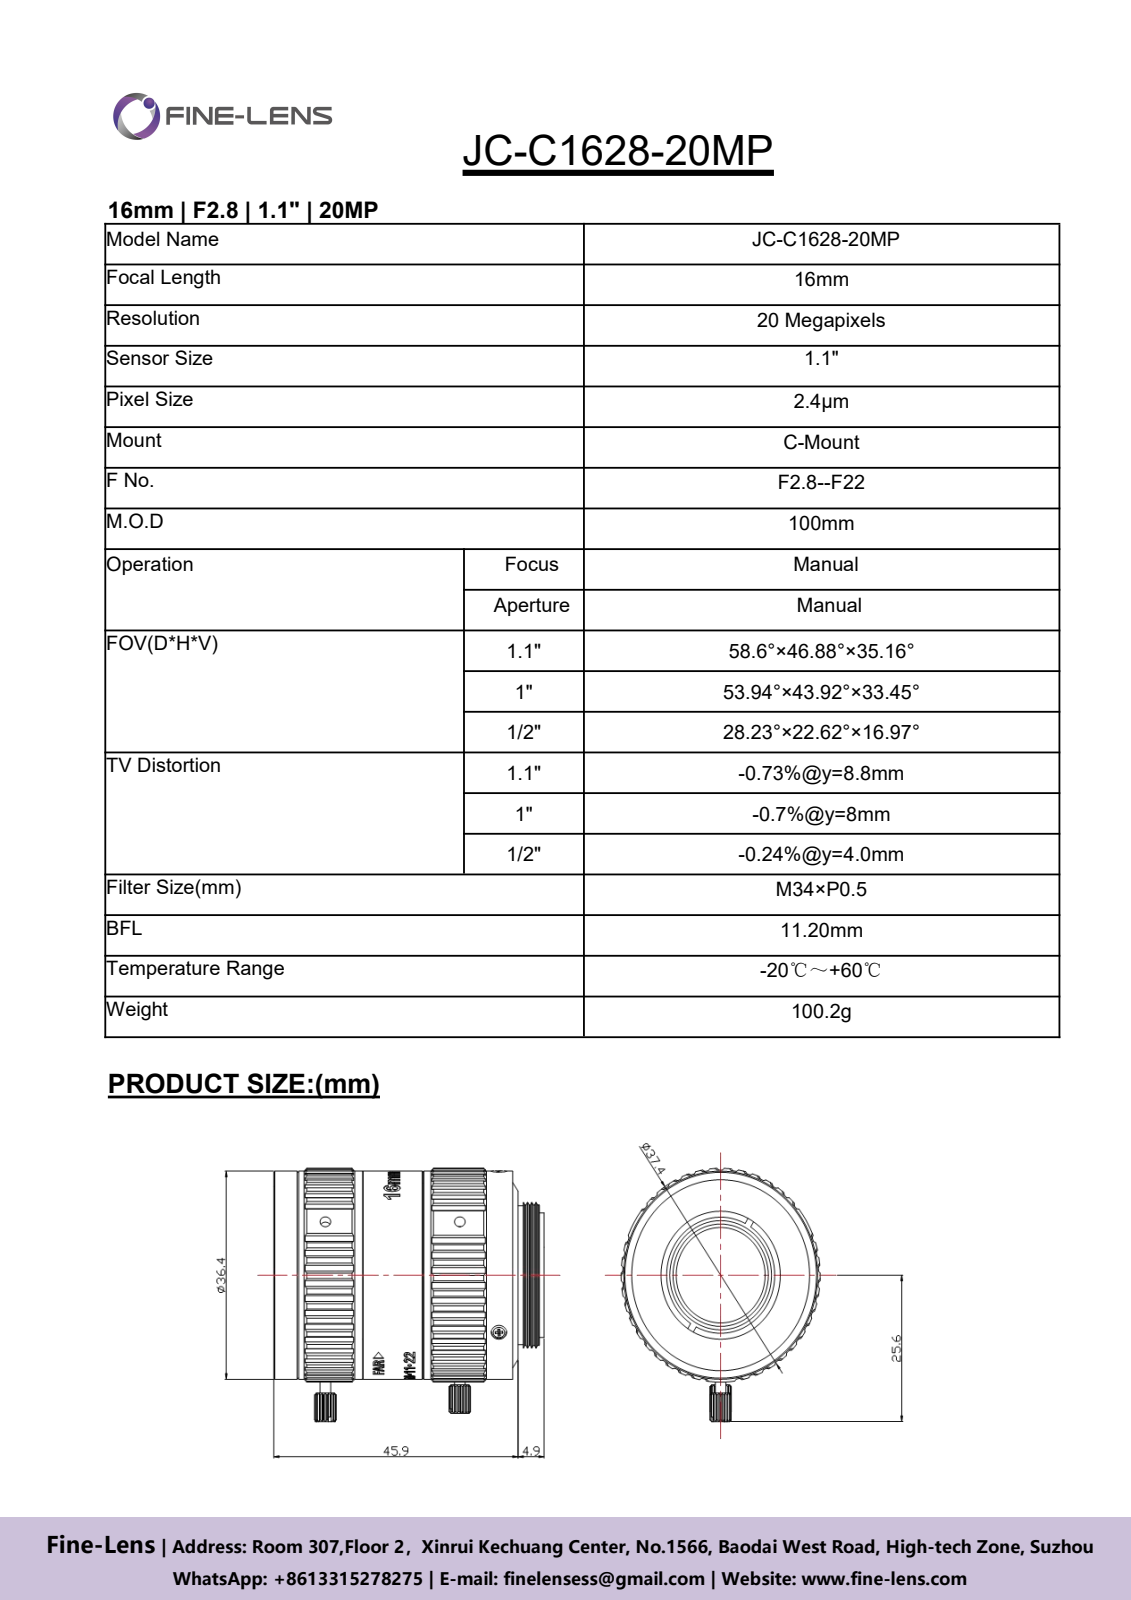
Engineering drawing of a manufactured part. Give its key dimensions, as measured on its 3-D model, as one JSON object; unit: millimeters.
{"part_name": "16MM_1_1INCH_ASM; 16MM_1_1INCH_ASM_ASM", "step_written_by": "CREO PARAMETRIC BY PTC INC, 2020053 (CONFIG_CONTROL_DESIGN)", "units": "millimeters", "bodies": {"solids": 1, "faces": 1450, "planar": 661, "cylindrical": 385, "other": 404}, "overall_size": [50.77, 41.66, 37.39], "volume_mm3": 24148, "surface_area_mm2": 26913, "round_holes": [[2, 6], [1.4, 4], [1.2, 3], [1.7, 3], [2.9, 3], [3, 3], [1.5, 2], [2.6, 2], [12.4, 1], [14.8, 1], [15.6, 1], [15.9, 1]], "round_bosses_or_shafts": [[2.75, 3], [2, 3], [36.4, 1], [35.2, 1], [34.5, 1], [34.5, 1], [33.6, 1], [28.3, 1]], "partial_cylinders_radius": [[0.5, 6], [1.25, 6], [1.5, 6], [1.73, 2], [1.91, 2], [2, 2], [0.98, 1], [1, 1]], "face_to_face_distances": [41.58, 27.17, 14.41, 4.2, 22.97, 37.38, 0.8, 1, 42.38, 38.18], "hole_center_spacings": [11.77, 21.52, 25.25, 33.29, 5.05, 16.53, 20.2, 3]}
